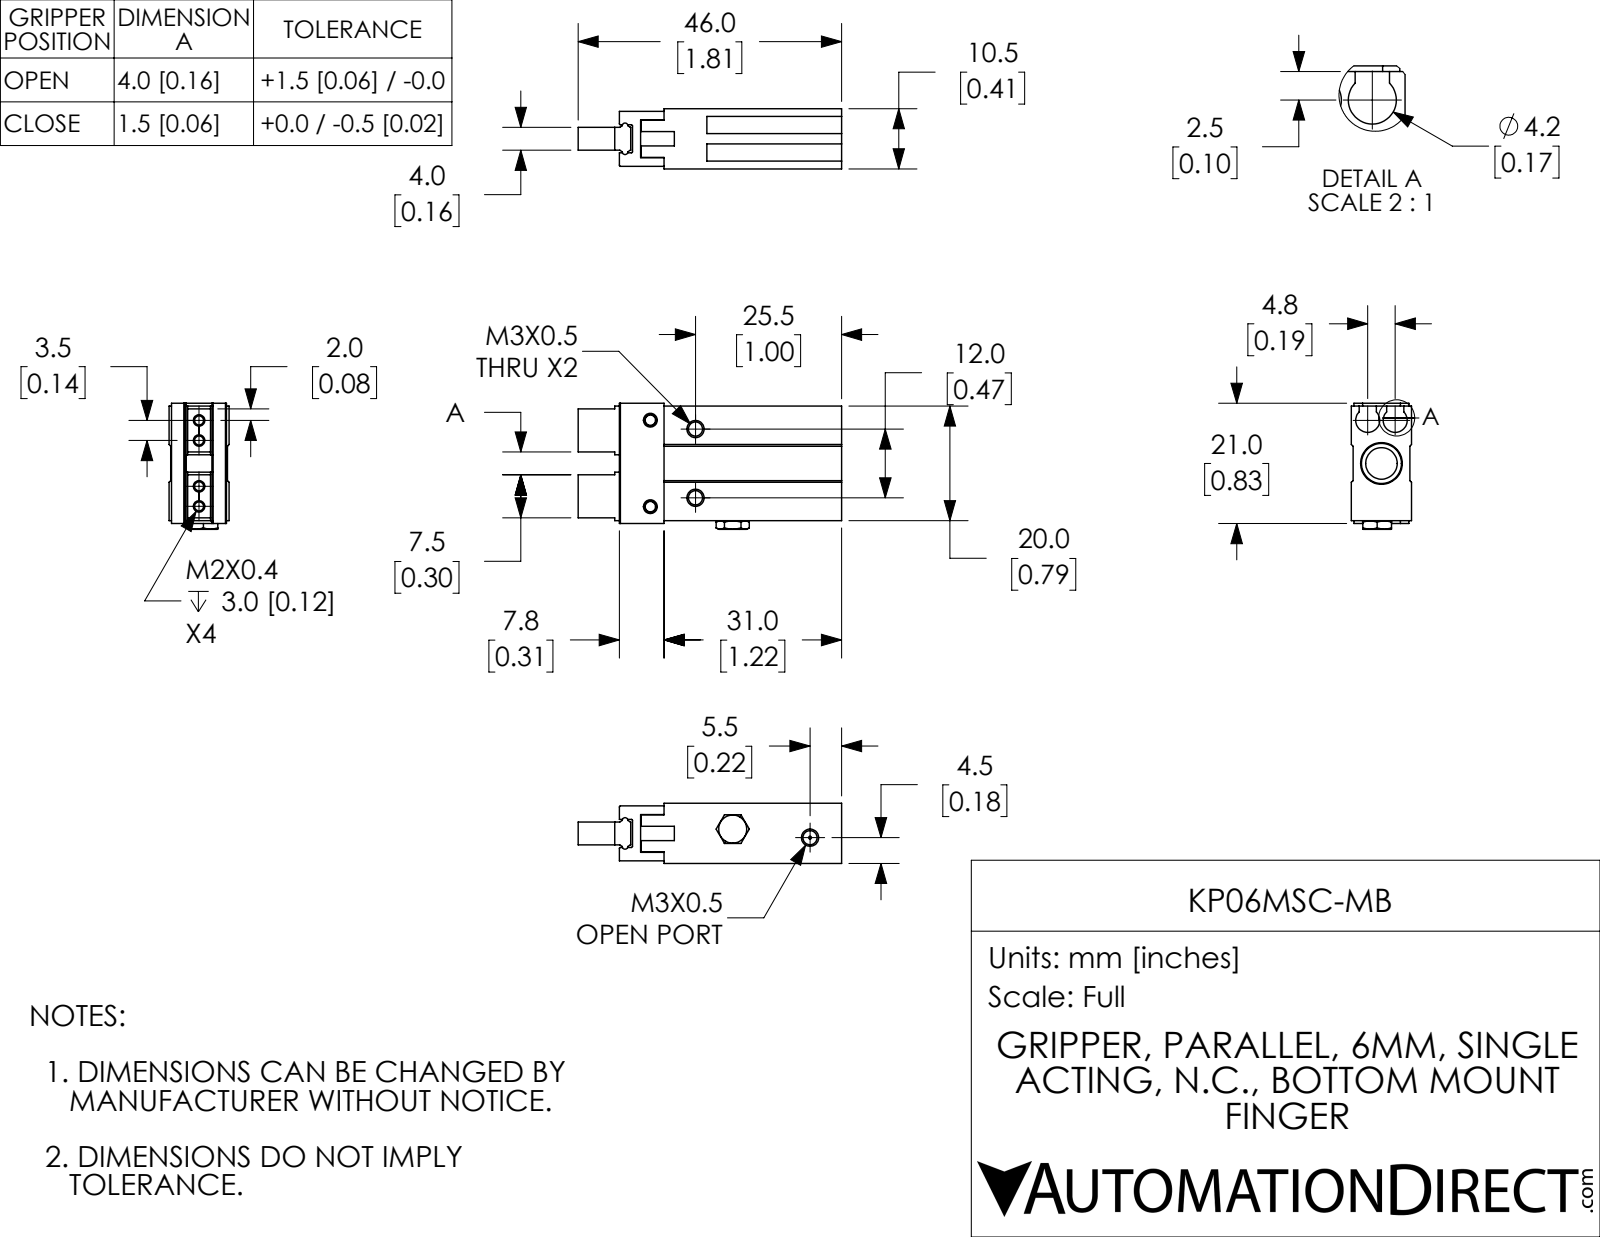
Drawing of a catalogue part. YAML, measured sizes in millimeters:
part_name: "KP06MSC-MB; KP06MSC-MB-3; KP06MSC-MB-2; KP06MSC-MB-1"
step_written_by: "SolidWorks 2017 (CONFIG_CONTROL_DESIGN)"
units: millimeters
bodies: {solids: 3, faces: 192, planar: 106, cylindrical: 44, other: 42}
overall_size: [46, 22, 10.5]
volume: 7013
surface_area: 5094
round_holes:
  - {diameter: 2.46, count: 3}
  - {diameter: 0.5, count: 2}
  - {diameter: 1.57, count: 2}
  - {diameter: 1.57, count: 2}
  - {diameter: 3.1, count: 2}
  - {diameter: 2.46, count: 1}
  - {diameter: 5.5, count: 1}
  - {diameter: 7, count: 1}
partial_cylinders:
  - {radius: 0.2, count: 4}
  - {radius: 0.5, count: 2}
  - {radius: 2.1, count: 2}
face_to_face_distances: [3.25, 2, 4, 10.5, 3.7, 10.2, 0.45, 6.5, 10.05, 9.75]
hole_center_spacings: [3.5, 4, 7.5, 11.5, 8, 12, 13.58, 15]
